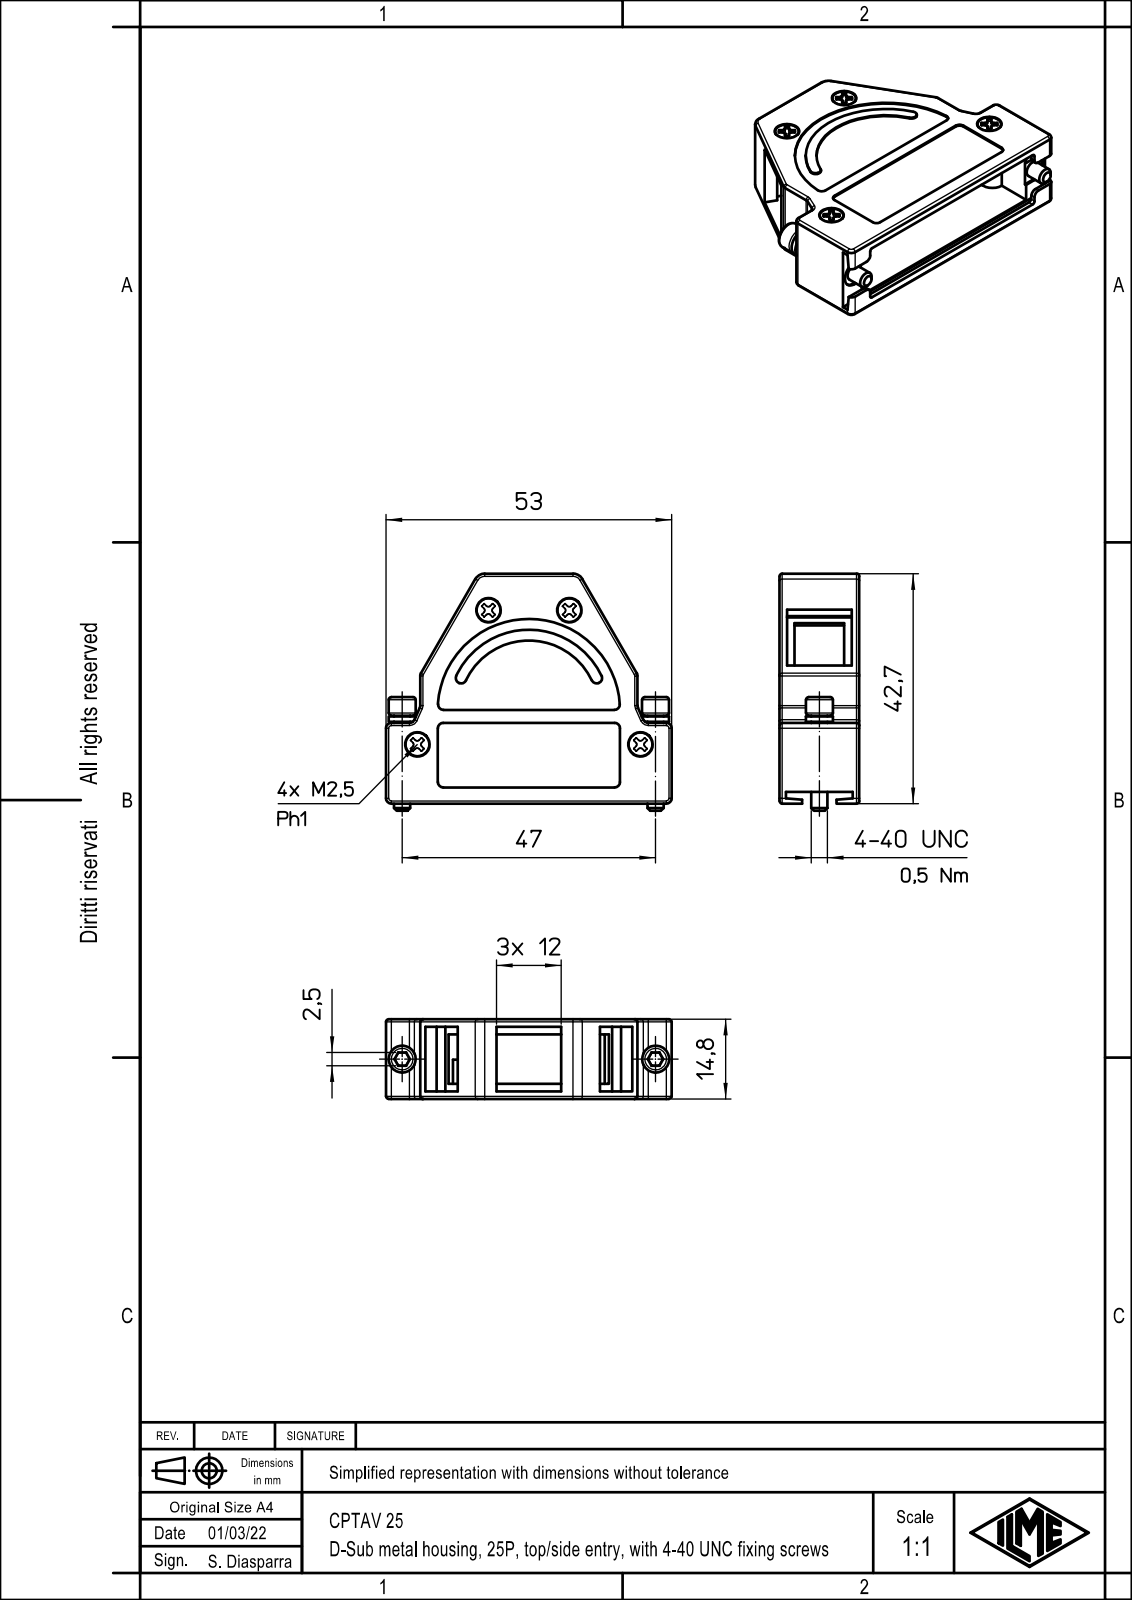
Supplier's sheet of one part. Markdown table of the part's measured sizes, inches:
| quantity | value |
| --- | --- |
| part name | CPTAV_25 |
| STEP written by | Creo Elements/Direct Modeling 20.1B 02-Apr-2019 (C) Parametric Technology GmbH (AUTOMOTIVE_DESIGN) |
| units | inches |
| bodies | 1 solid, 722 faces (169 planar, 213 cylindrical, 340 other) |
| overall size | 2.087 × 1.732 × 0.583 |
| volume | 0.543 in³ |
| surface area | 15.28 in² |
| round bosses / shafts (diameter × count) | 0.197 × 2, 0.118 × 2 |
| partial cylindrical surfaces (radius × count) | 0.02 × 42, 0.039 × 22, 0.079 × 3, 0.031 × 2, 0.096 × 2, 0.508 × 1, 0.587 × 1, 0.665 × 1 |
| main face-to-face distances | 0.051, 0.516, 0.059, 0.524, 0.575, 0.465, 0.567, 0.583, 0.047, 0.055 |
